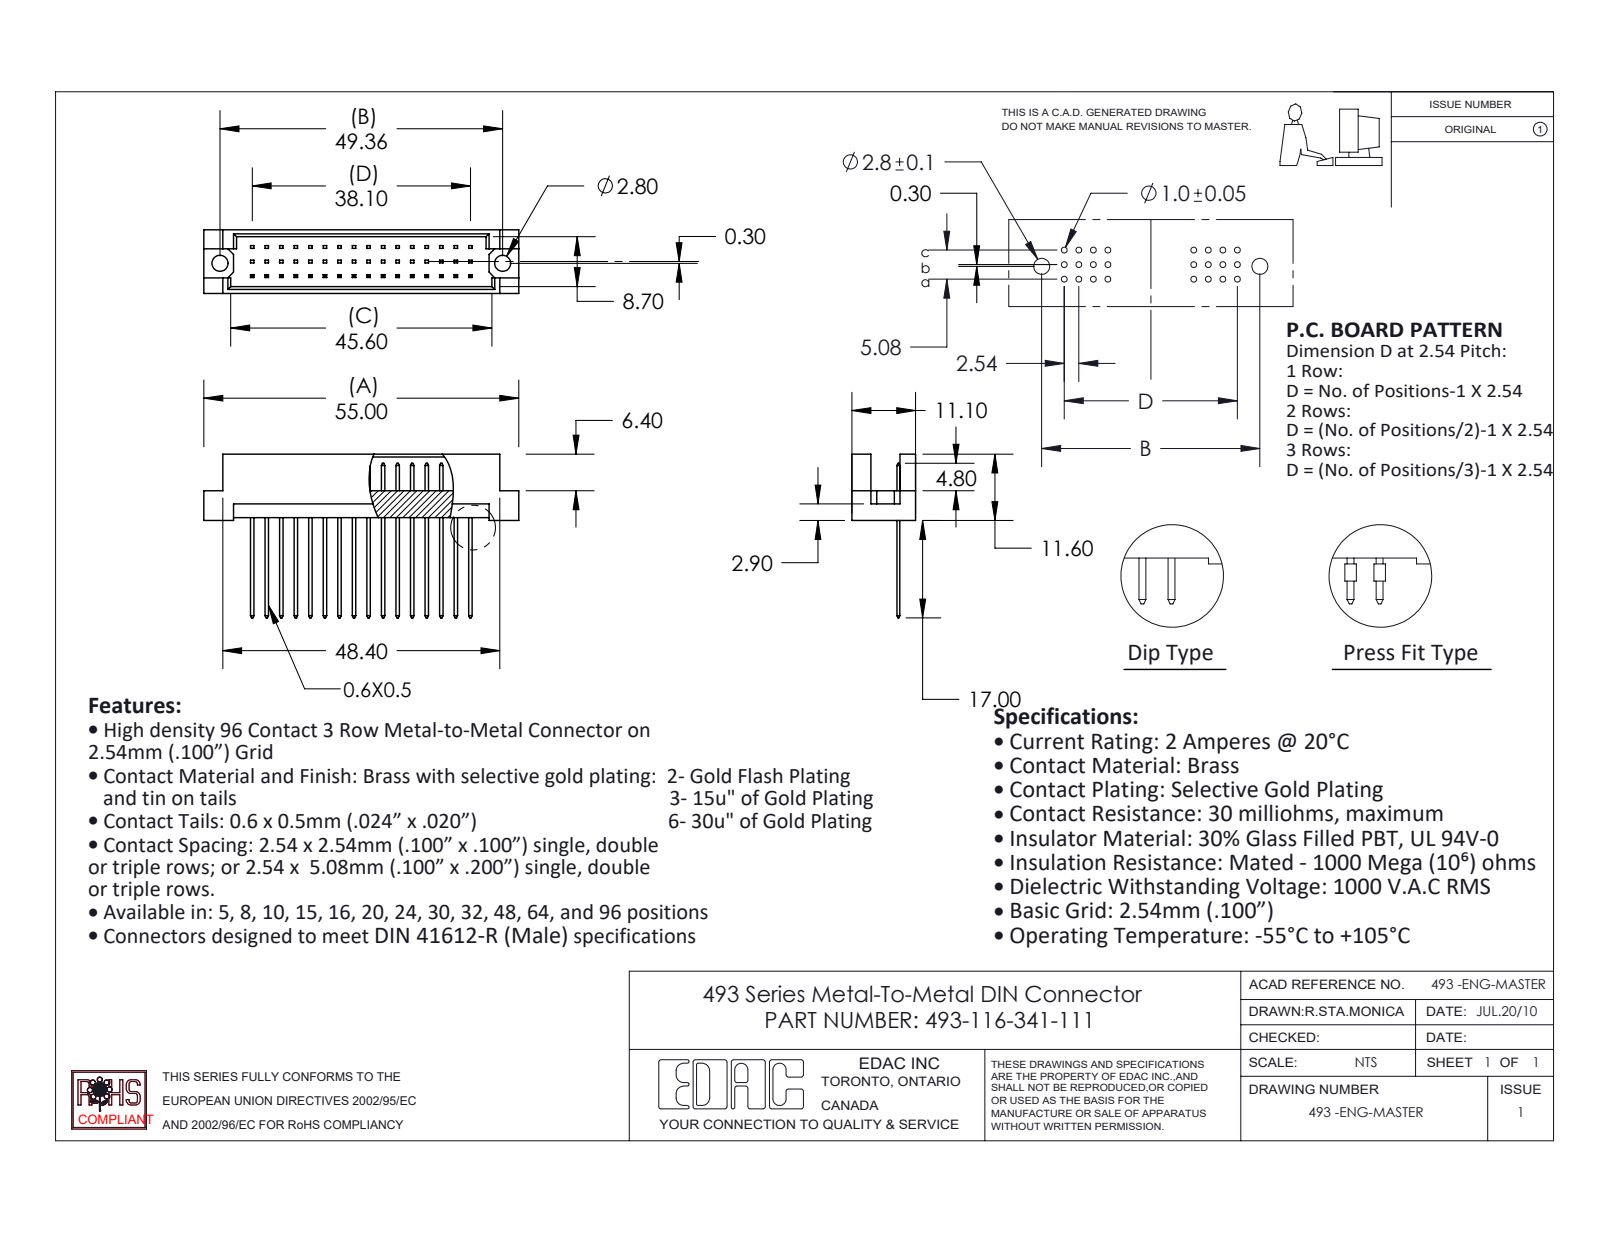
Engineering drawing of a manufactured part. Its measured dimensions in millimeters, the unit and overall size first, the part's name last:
Units: millimetres
Overall size (bounding box): 55 × 28.6 × 11.1
Round holes (diameter × count): ⌀2.8 ×2
Main face-to-face distances: 1.2, 9.9, 11.1, 0.5, 2.54, 8.7, 5.08, 4.7, 2.76, 8.34
Hole centre spacings: 49.36
Volume: 3 400 mm³ · Surface area: 4 701 mm²
Bodies: 17 solids, 468 faces (464 planar, 4 cylindrical, 0 other)
Part name (STEP PRODUCT): 493 Part_48; 493-116-341-111; 493-290_41
STEP written by: SolidWorks 2020 (CONFIG_CONTROL_DESIGN)
